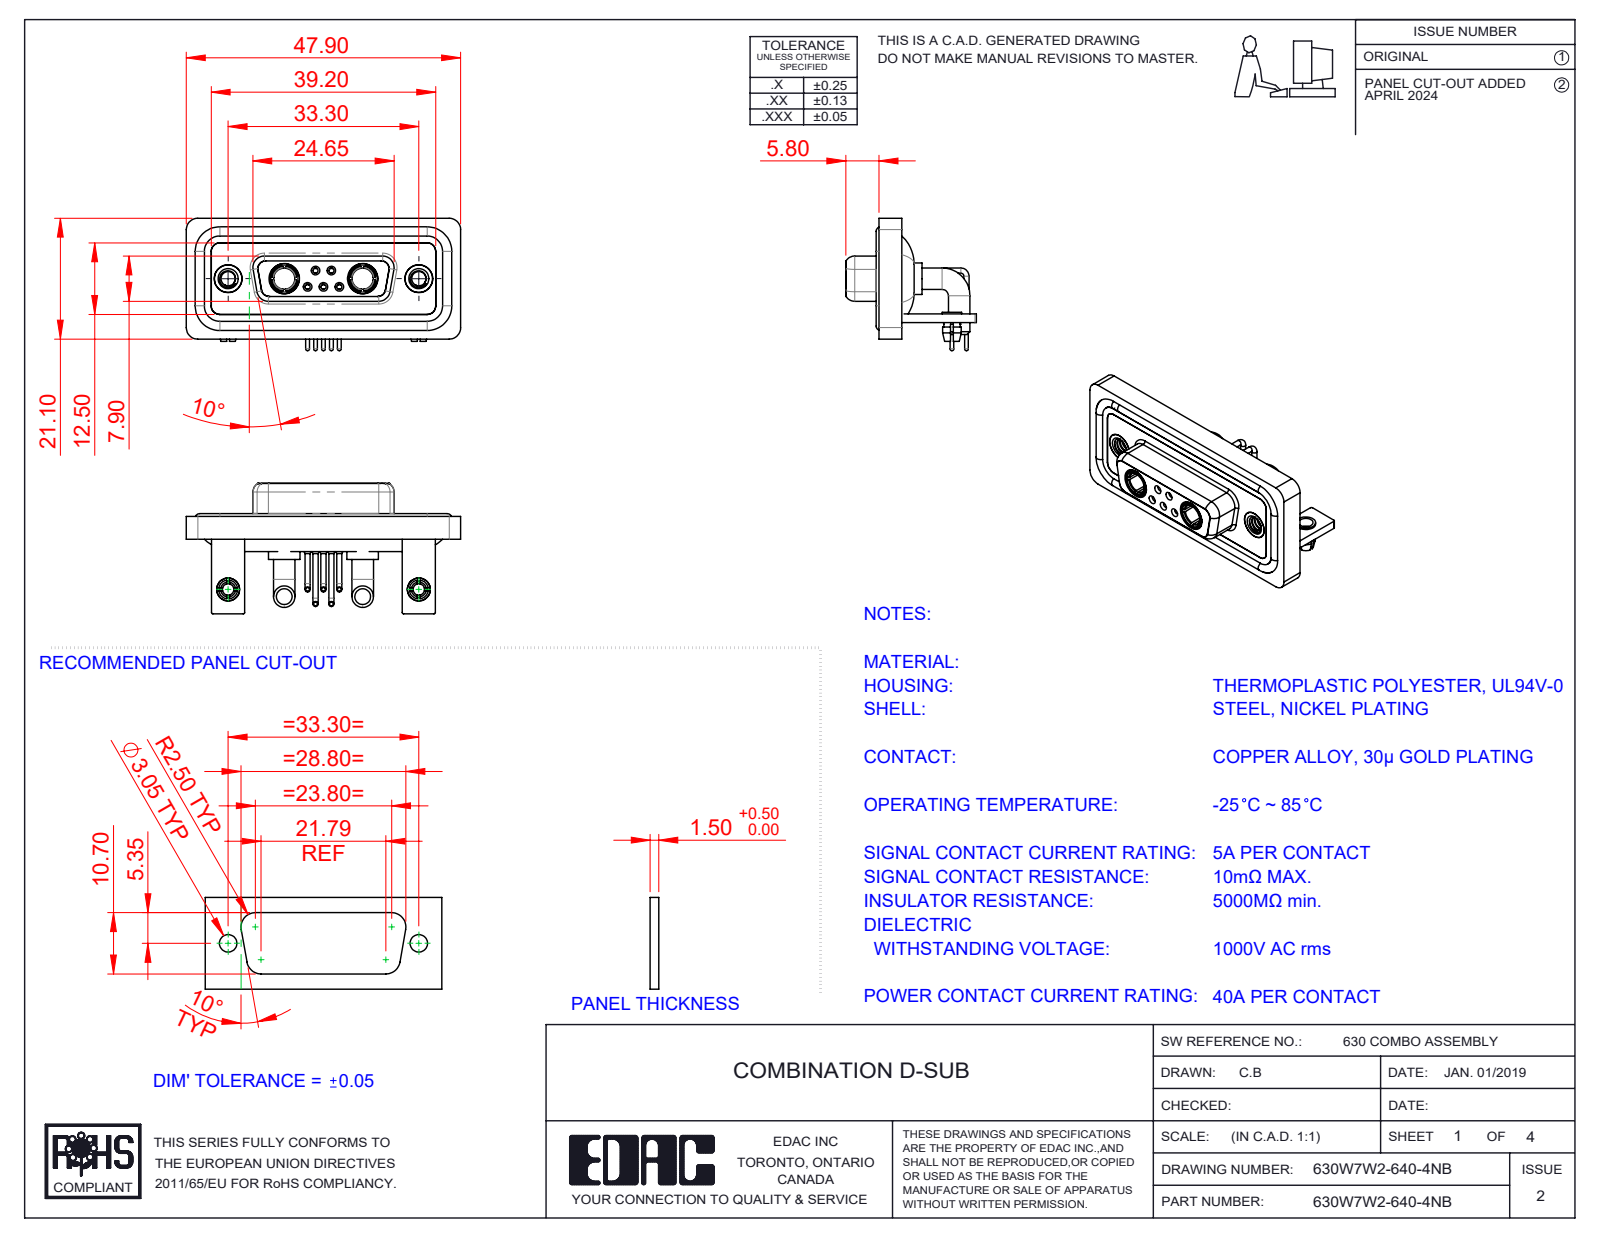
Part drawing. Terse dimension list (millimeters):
name: 630Combo Shell Front_15 Contacts; 630Combo Stabilizer Bracket_50 Contacts; Power Socket_40A RA; 630Combo Board Lock_50 Contacts (+7 more)
written by: SolidWorks 2023 (CONFIG_CONTROL_DESIGN)
unit: mm
bodies: 20 solids, 941 faces (306 planar, 407 cylindrical, 228 other)
size: 47.9 × 23.12 × 22.8
volume: 6 737 mm³; area: 11 242 mm²
holes: 7× ⌀2, 5× ⌀0.9, 5× ⌀1.1, 5× ⌀1.5, 4× ⌀2.5, 4× ⌀4.85, 3× ⌀1.6, 2× ⌀1.7, 2× ⌀3.2, 2× ⌀3.7, 2× ⌀4, 2× ⌀4.05
bosses: 6× ⌀1.6, 5× ⌀0.9, 5× ⌀0.65, 4× ⌀3.75, 2× ⌀5.5, 2× ⌀5.2, 2× ⌀4.96, 2× ⌀4.95
rounds: 21× R2, 18× R1.5, 16× R0.25, 12× R1.35, 8× R1.6, 5× R0.5, 4× R0.6, 4× R0.65
face distances: 0.4, 2.9, 1.5, 1.8, 3.7, 1.1, 4.1, 1.6, 2.5, 1.4
hole spacings: 3.16, 2.77, 9.8, 23.5, 33.3, 4.31, 4.33, 5.03
